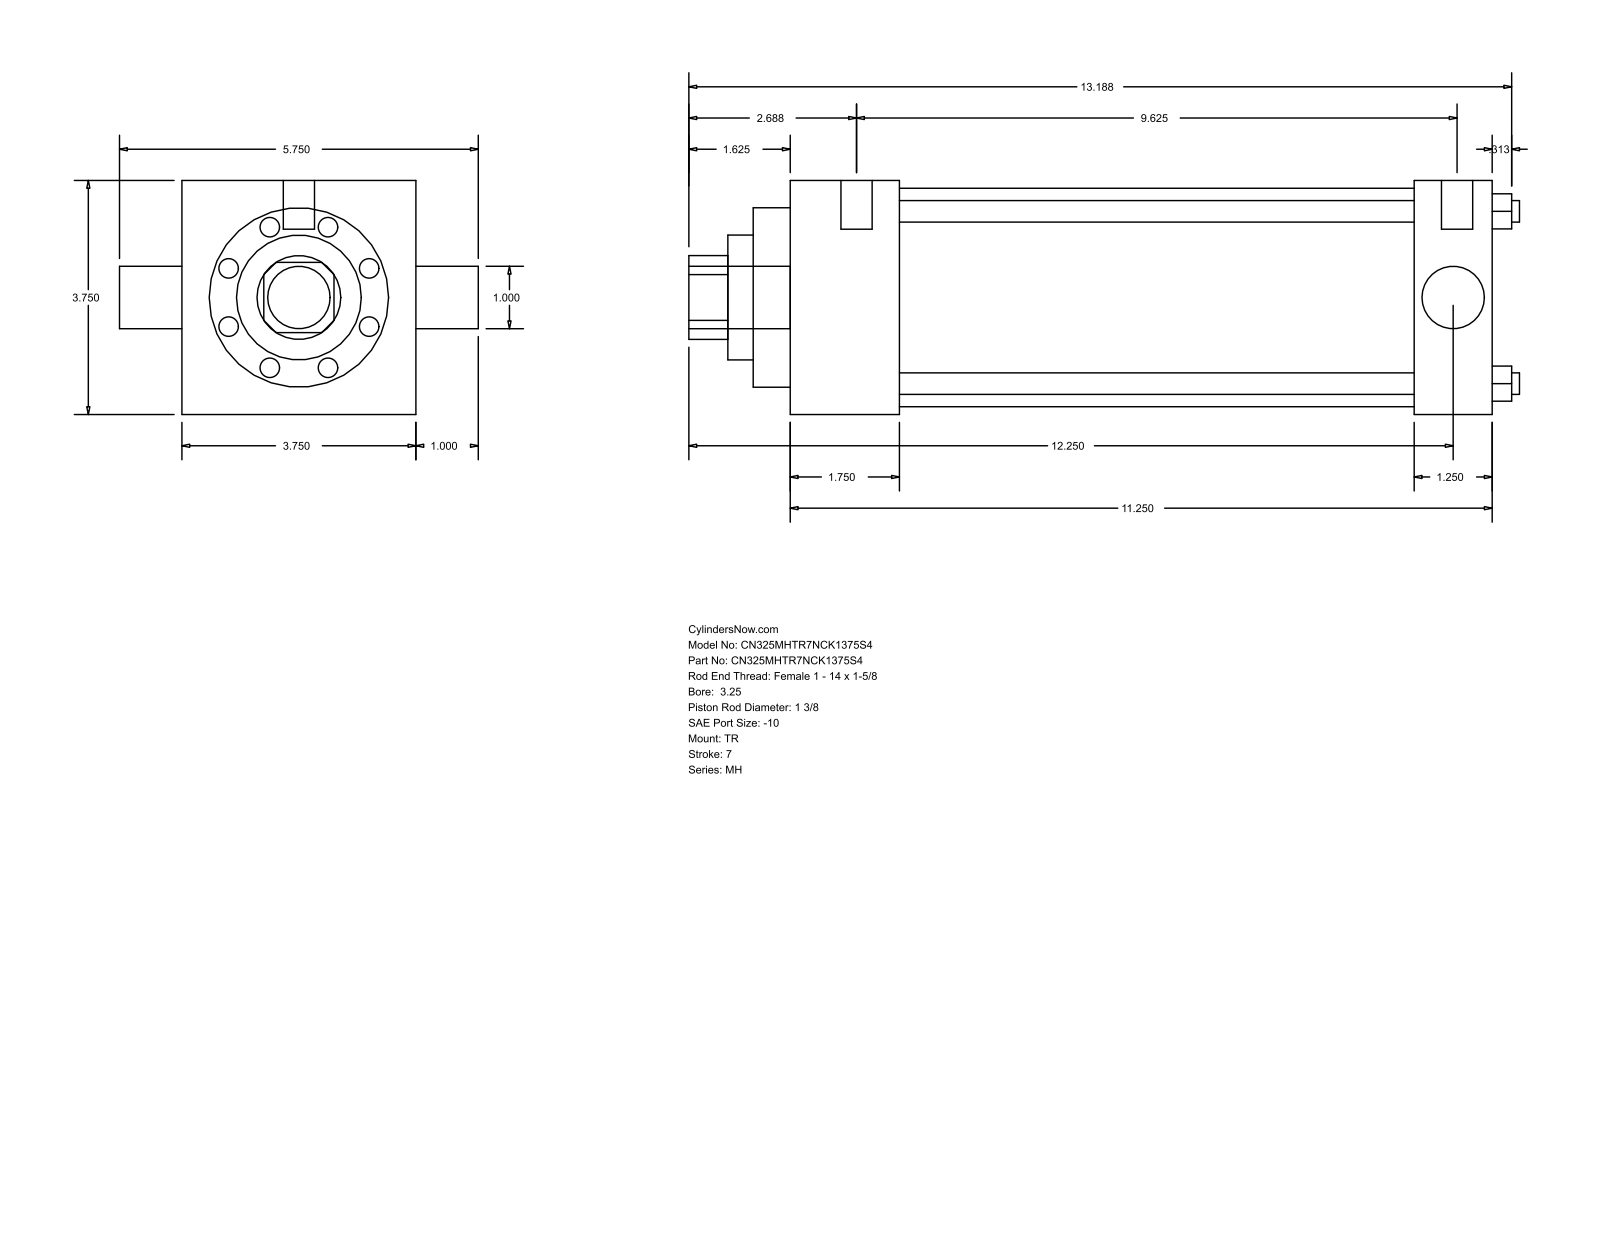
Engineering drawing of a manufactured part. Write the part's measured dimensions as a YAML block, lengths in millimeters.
part_name: "MH_TR__0325_1.375"
step_written_by: "GSSL Pune (CONFIG_CONTROL_DESIGN)"
units: millimeters
bodies: {solids: 0, faces: 86, planar: 61, cylindrical: 25, other: 0}
overall_size: [338.14, 146.05, 95.25]
round_holes:
  - {diameter: 8.76, count: 4}
  - {diameter: 25.4, count: 1}
  - {diameter: 34.92, count: 1}
  - {diameter: 50.8, count: 1}
  - {diameter: 73.03, count: 1}
  - {diameter: 88.9, count: 1}
round_bosses_or_shafts:
  - {diameter: 5.56, count: 3}
  - {diameter: 12.7, count: 2}
  - {diameter: 25.4, count: 1}
partial_cylinders:
  - {radius: 17.06, count: 1}
face_to_face_distances: [95.24, 285.75, 44.45, 254, 209.55, 241.3, 31.75, 15.08, 59.53, 269.08]
hole_center_spacings: [49.57, 70.1, 99.14]
